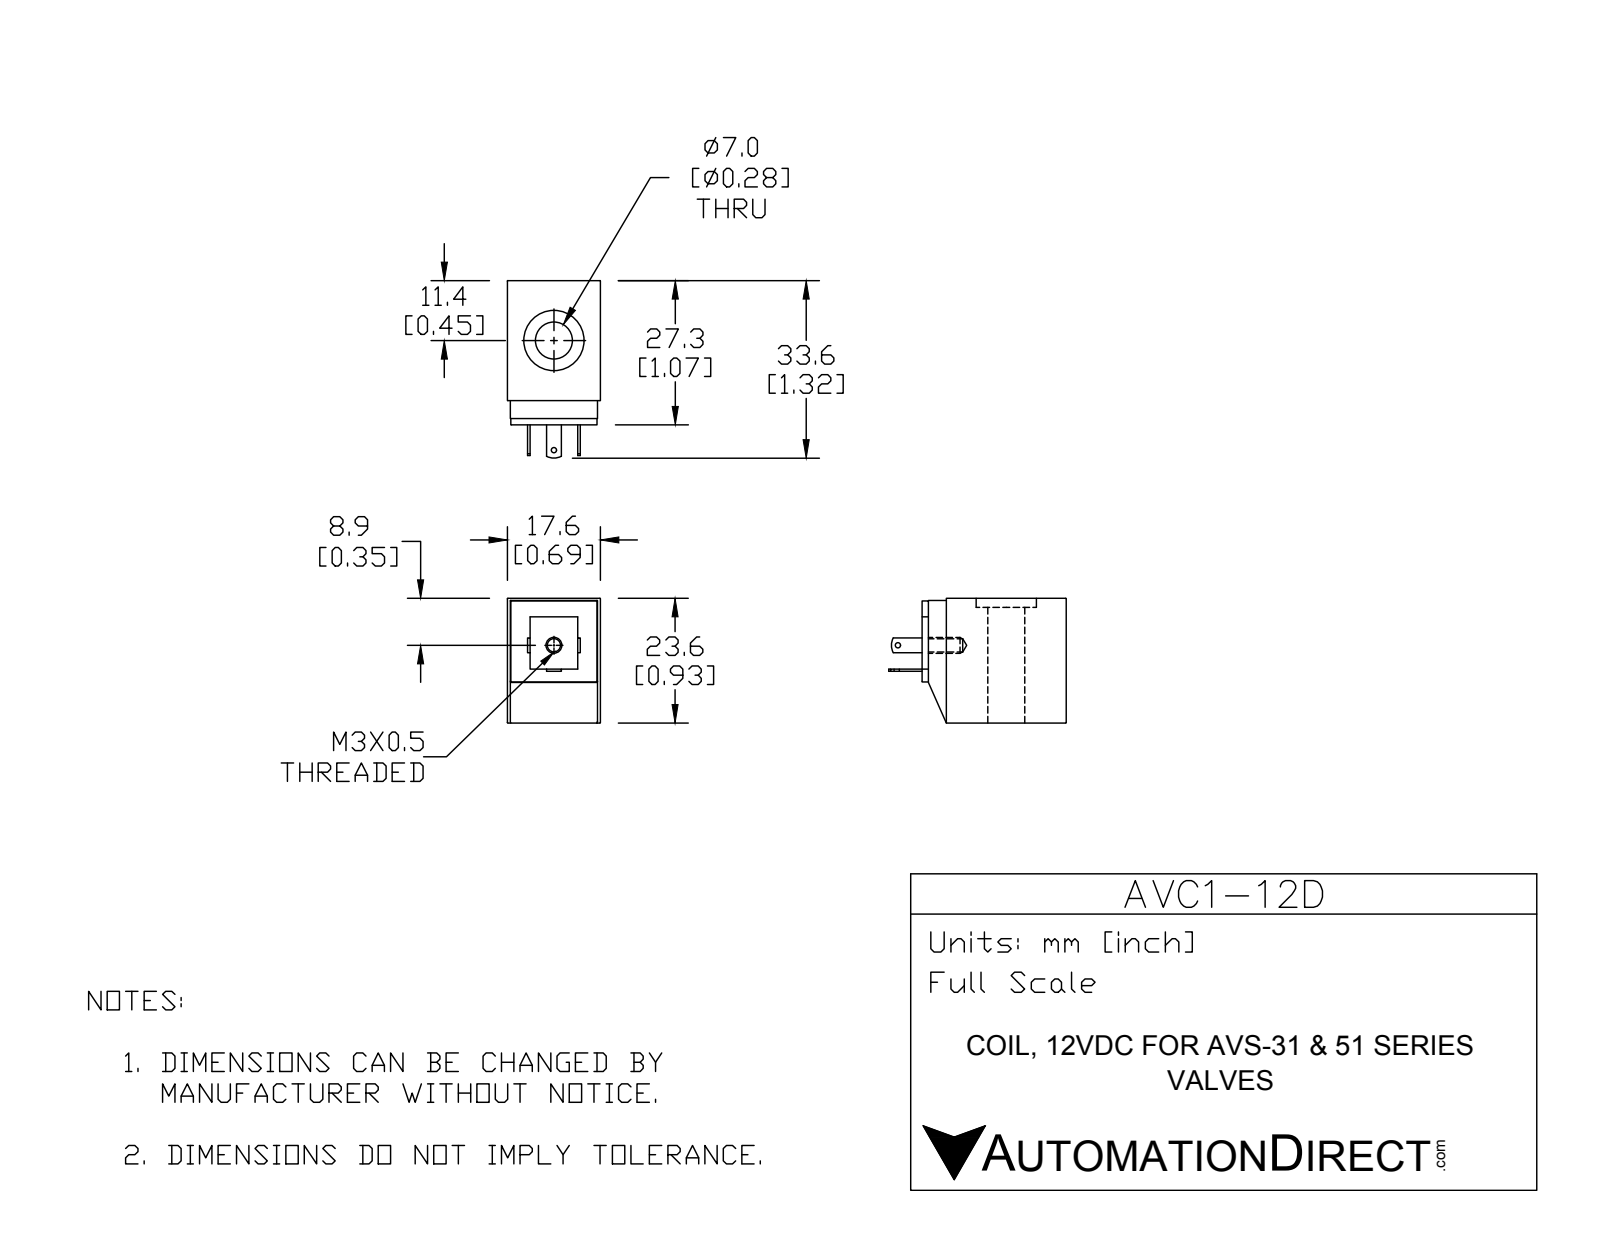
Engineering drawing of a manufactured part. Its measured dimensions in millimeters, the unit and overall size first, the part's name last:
Units: millimetres
Overall size (bounding box): 33.6 × 23.6 × 17.6
Round holes (diameter × count): ⌀1 ×2, ⌀2.5 ×1, ⌀7 ×1, ⌀11.4 ×1
Partial cylindrical surfaces — rounded edges, fillets, slot ends (radius × count): R0.1 ×16, R3 ×2
Main face-to-face distances: 17.6, 23.6, 27.3, 0.55, 17.05, 1.2, 26.1, 13.3, 0.4, 16.5
Hole centre spacings: 20.75
Volume: 9 679 mm³ · Surface area: 3 645 mm²
Bodies: 1 solid, 69 faces (31 planar, 32 cylindrical, 6 other)
Part name (STEP PRODUCT): AVC1-12D
STEP written by: SolidWorks 2016 (AUTOMOTIVE_DESIGN)
